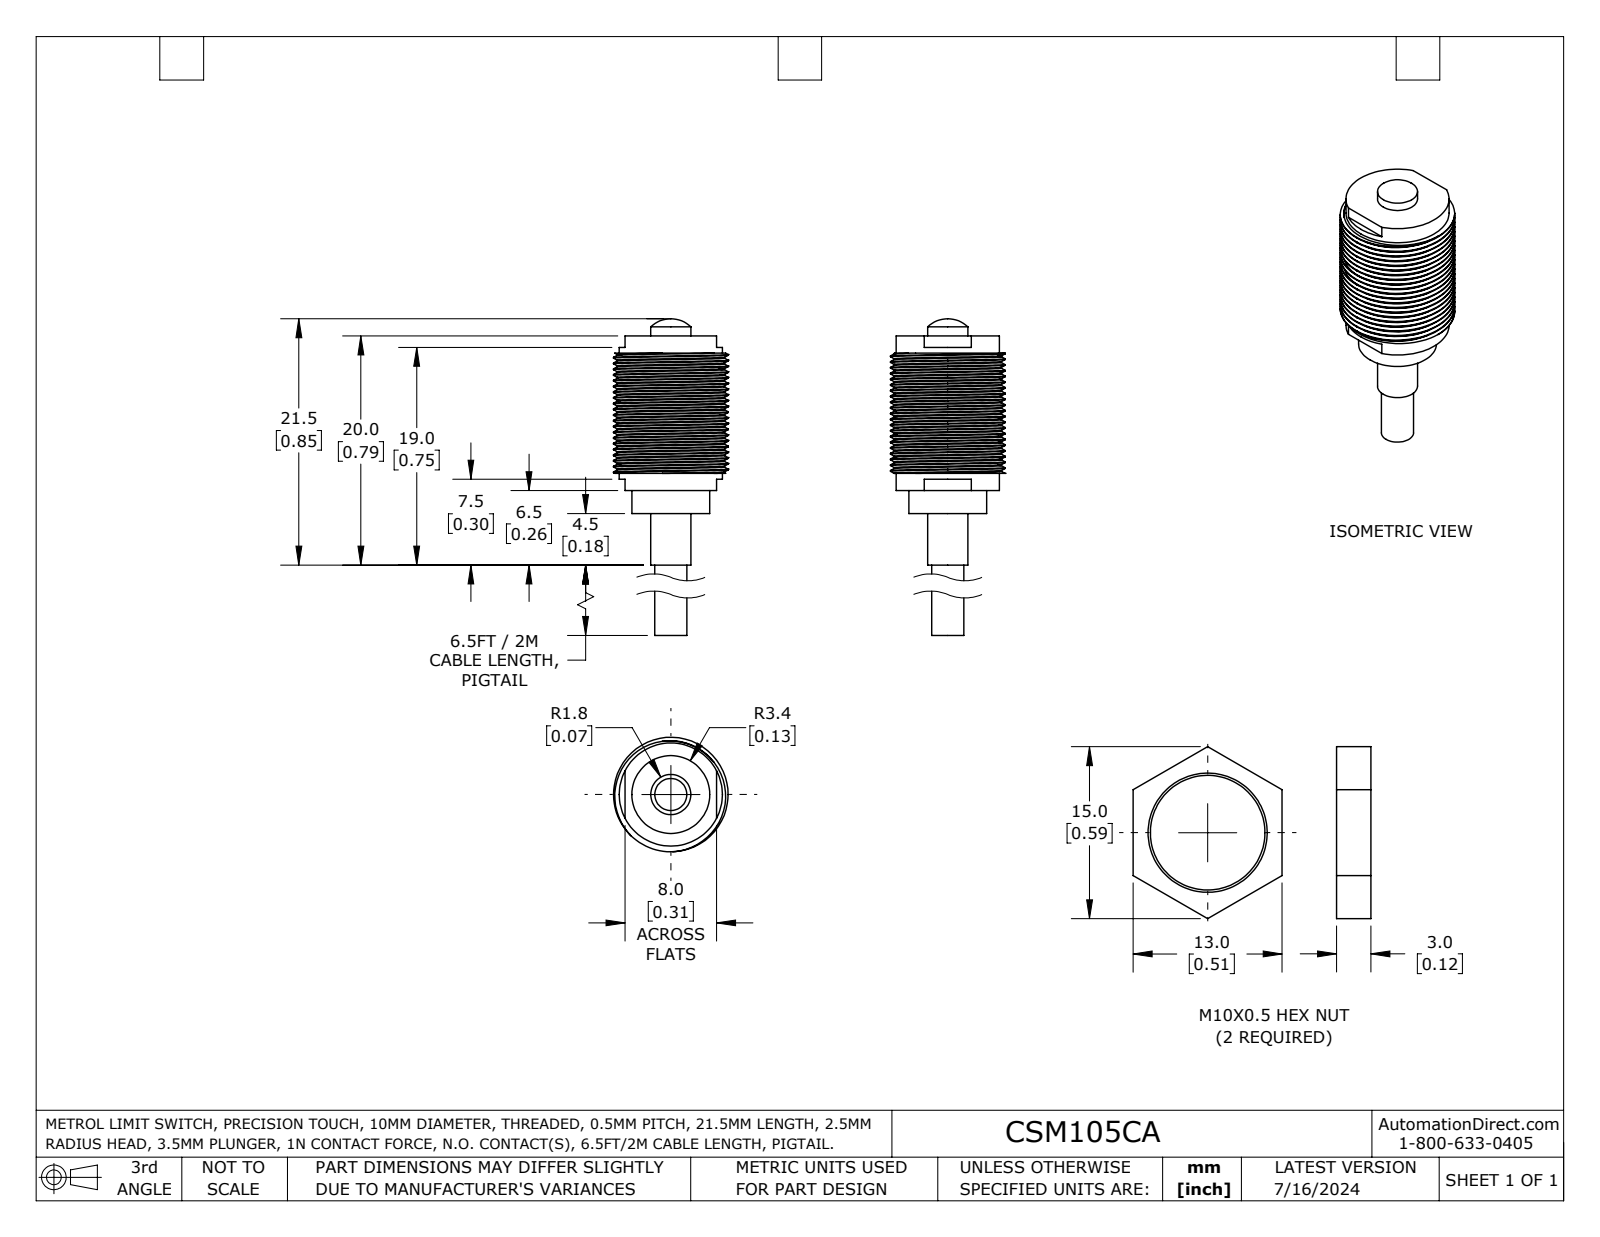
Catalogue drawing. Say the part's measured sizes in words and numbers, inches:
The part is named "CSM105CA". Its 3-D file was written by "SolidWorks 2023 (AUTOMOTIVE_DESIGN)". It is 1 solid with 75 faces: 15 planar, 55 cylindrical and 5 other. Overall it measures 1.043 by 0.394 by 0.394 inches. Its volume is 0.068 cubic inches and its surface area 1.473 square inches. Round bosses or shafts: 1 of diameter 0.394, 1 of diameter 0.354, 1 of diameter 0.268, 1 of diameter 0.138, 1 of diameter 0.11. The main face-to-face distances are 0.61, 0.079, 0.531, 0.059, 0.472, 0.315, 0.551, 0.138, 0.413, 0.453.
